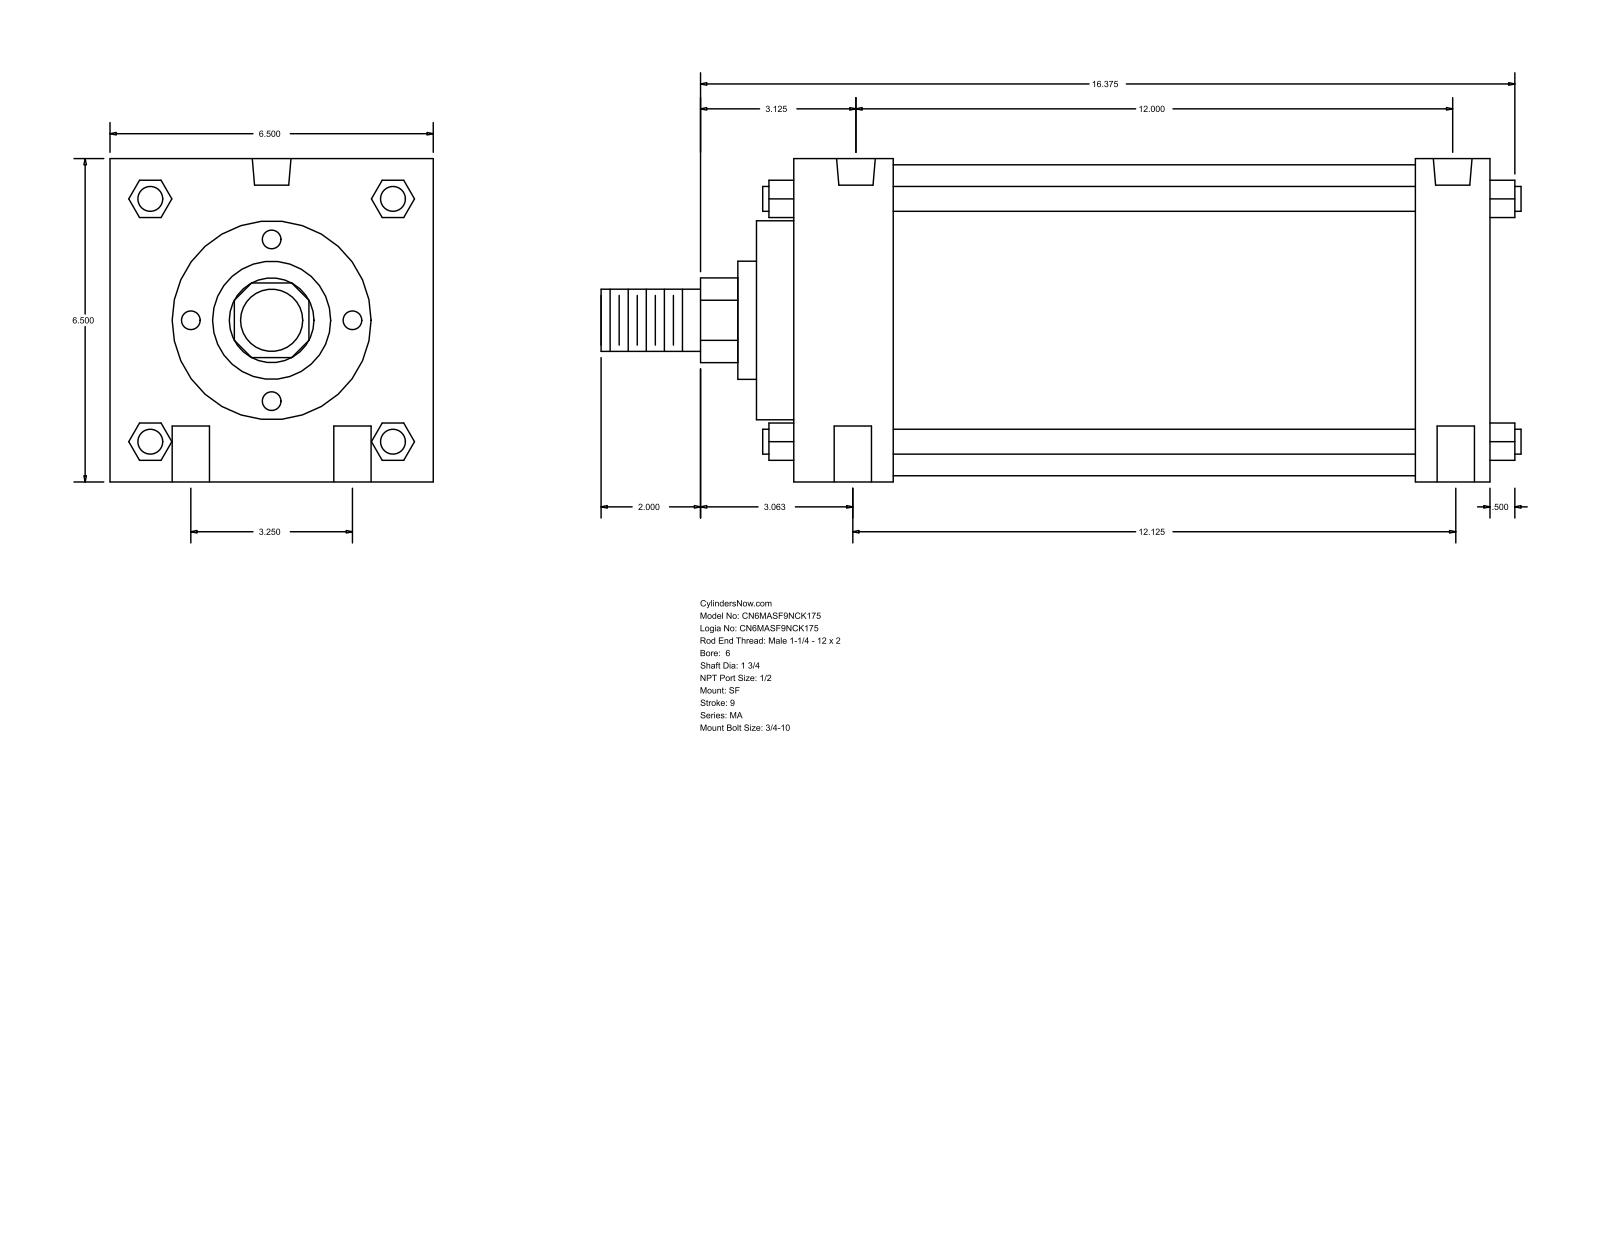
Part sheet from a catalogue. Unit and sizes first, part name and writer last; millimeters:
Units: millimetres
Overall size (bounding box): 469.9 × 165.1 × 165.1
Round holes (diameter × count): ⌀19.05 ×4, ⌀17.46 ×2, ⌀19.77 ×2
Round bosses / shafts (diameter × count): ⌀12.7 ×4, ⌀158.75 ×1, ⌀101.6 ×1, ⌀60.33 ×1, ⌀44.45 ×1, ⌀31.75 ×1
Partial cylindrical surfaces — rounded edges, fillets, slot ends (radius × count): R21.63 ×1
Main face-to-face distances: 165.1, 355.61, 19.05, 50.8, 317.5, 38.11, 266.7, 304.81, 69.85, 336.55
Hole centre spacings: 41.3, 82.54, 304.8, 307.97, 309.15, 309.16, 318.84
Bodies: 0 solids, 126 faces (95 planar, 31 cylindrical, 0 other)
Part name (STEP PRODUCT): MA_SF__0600_1.75
STEP written by: GSSL Pune (CONFIG_CONTROL_DESIGN)
